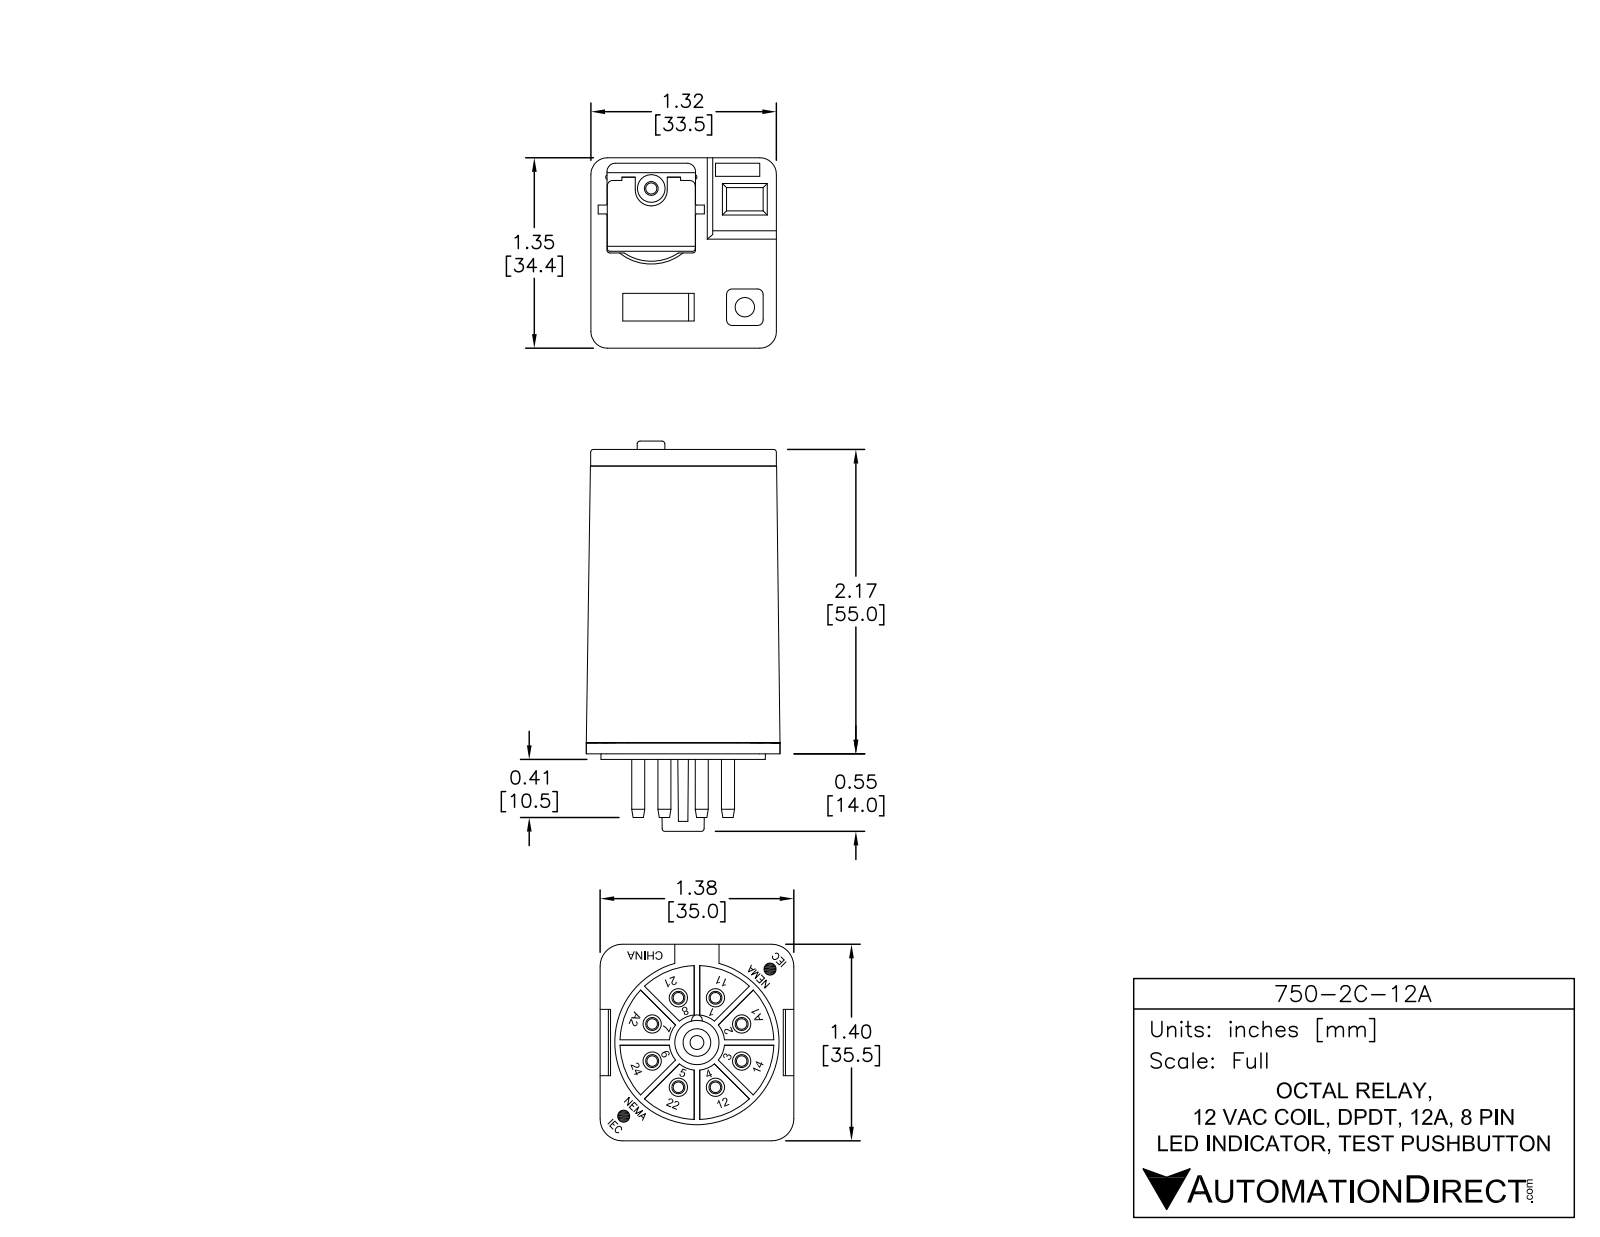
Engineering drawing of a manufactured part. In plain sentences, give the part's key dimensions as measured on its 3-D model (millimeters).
The part is named "750-2C-12A". Its 3-D file was written by "SolidWorks 2013 (AUTOMOTIVE_DESIGN)". It is 5 solids with 344 faces: 185 planar, 86 cylindrical and 73 other. Overall it measures 69.6 by 35.12 by 35 millimeters. Its volume is 67 512 cubic millimeters and its surface area 16 450 square millimeters. Round holes: 1 of diameter 2.5, 1 of diameter 27.5. Round bosses or shafts: 8 of diameter 3, 8 of diameter 2.3, 1 of diameter 29.5, 1 of diameter 8, 1 of diameter 4.8, 1 of diameter 0.83. Partial cylindrical surfaces (rounded edges, fillets, slot ends): 4 of radius 0.5, 4 of radius 3, 2 of radius 0.25, 2 of radius 1, 1 of radius 0.75, 1 of radius 0.99, 1 of radius 2.5, 1 of radius 5. The main face-to-face distances are 35, 50, 54.75, 3, 1.75, 51.75, 53, 1, 53.35, 1.4. The hole center spacings are 12.69.
